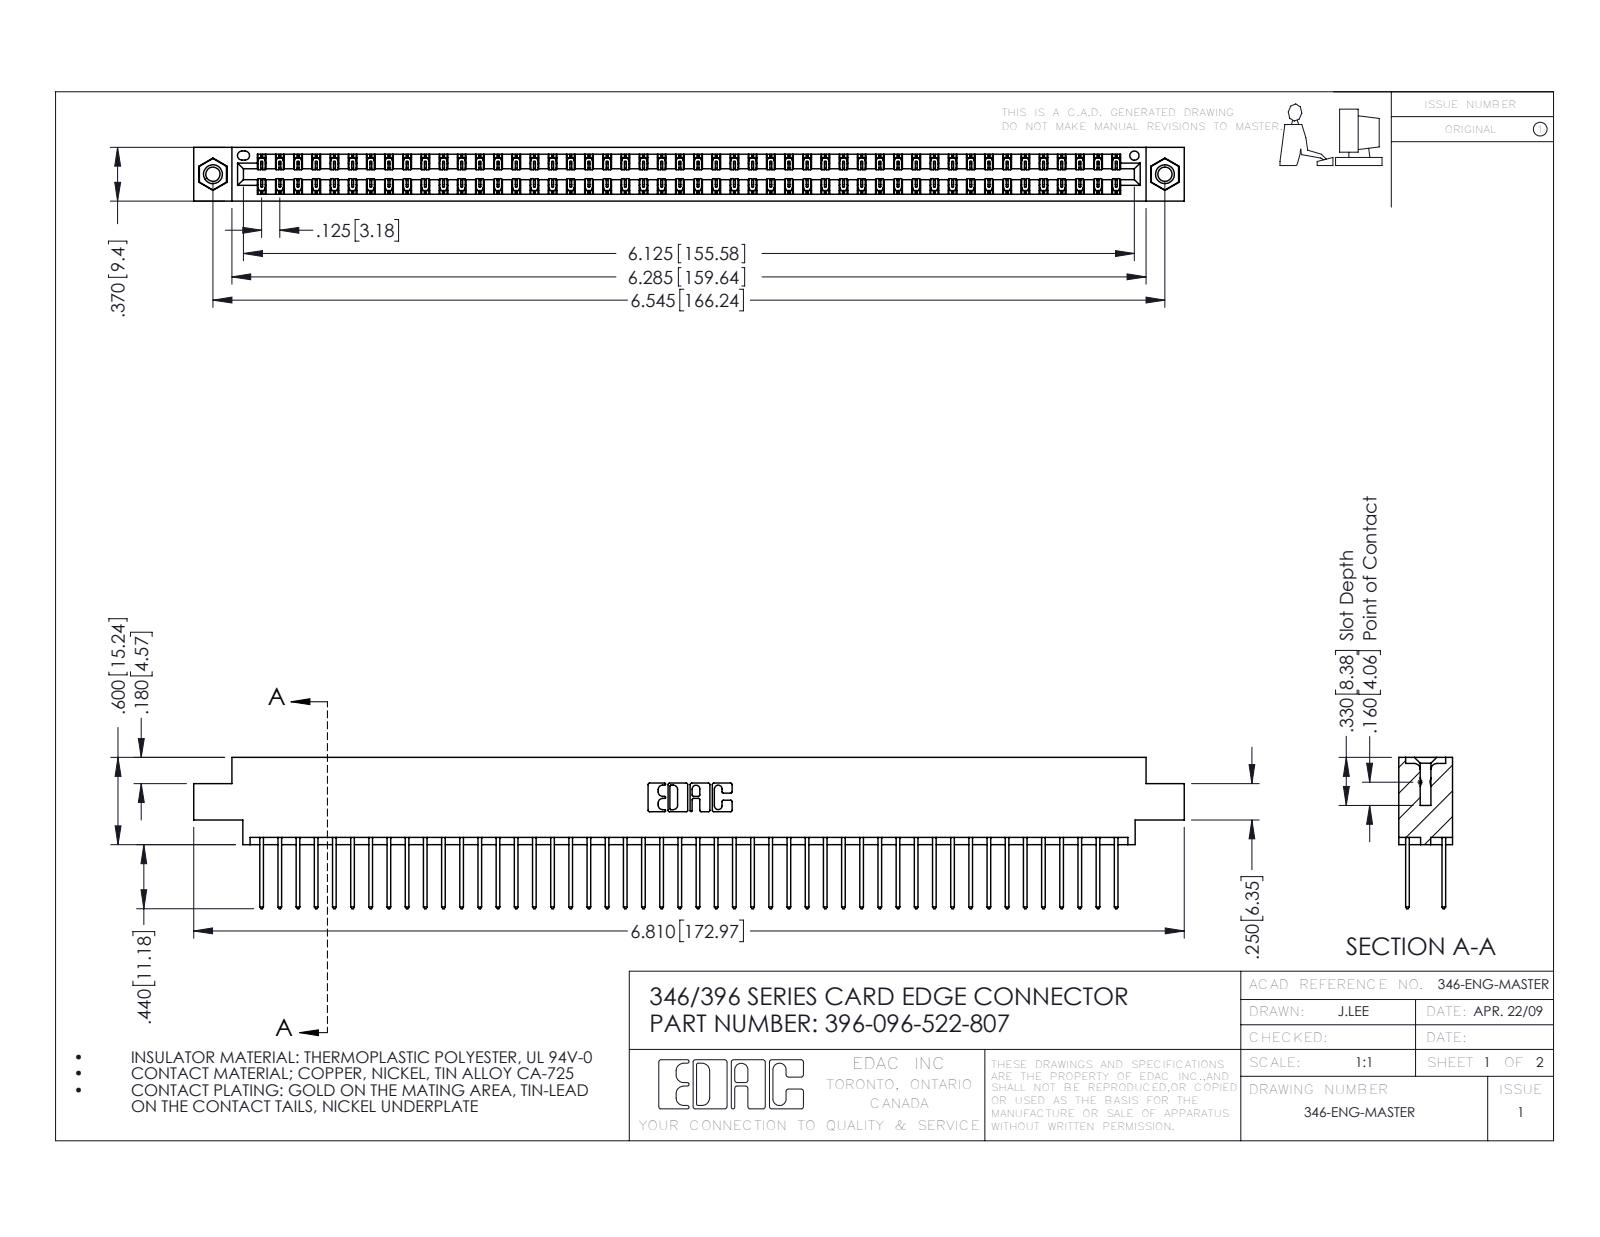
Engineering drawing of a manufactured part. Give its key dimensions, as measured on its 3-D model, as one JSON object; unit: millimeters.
{"part_name": "396-096-522-807; 345-292-001_345-293-122; 345-250-001_345-250-005-103; 346 Part_0.170 Offset - 0.156 Dia-TI", "step_written_by": "SolidWorks 2016 (CONFIG_CONTROL_DESIGN)", "units": "millimeters", "bodies": {"solids": 99, "faces": 5178, "planar": 3472, "cylindrical": 1690, "other": 16}, "overall_size": [173, 26.4, 9.4], "volume_mm3": 16990, "surface_area_mm2": 24810, "round_holes": [[2.5, 2], [3.2, 2], [4, 2], [1.6, 1]], "round_bosses_or_shafts": [[3.9, 2]], "partial_cylinders_radius": [[0.2, 144], [0.3, 96], [0.3, 22], [0.2, 6], [0.8, 6], [0.7, 3], [0.4, 2], [0.6, 2]], "face_to_face_distances": [1.2, 8.2, 6.4, 9.4, 1.8, 7.6, 0.6, 7, 5.6, 3.8], "hole_center_spacings": [6.2, 160.9, 166.2]}
